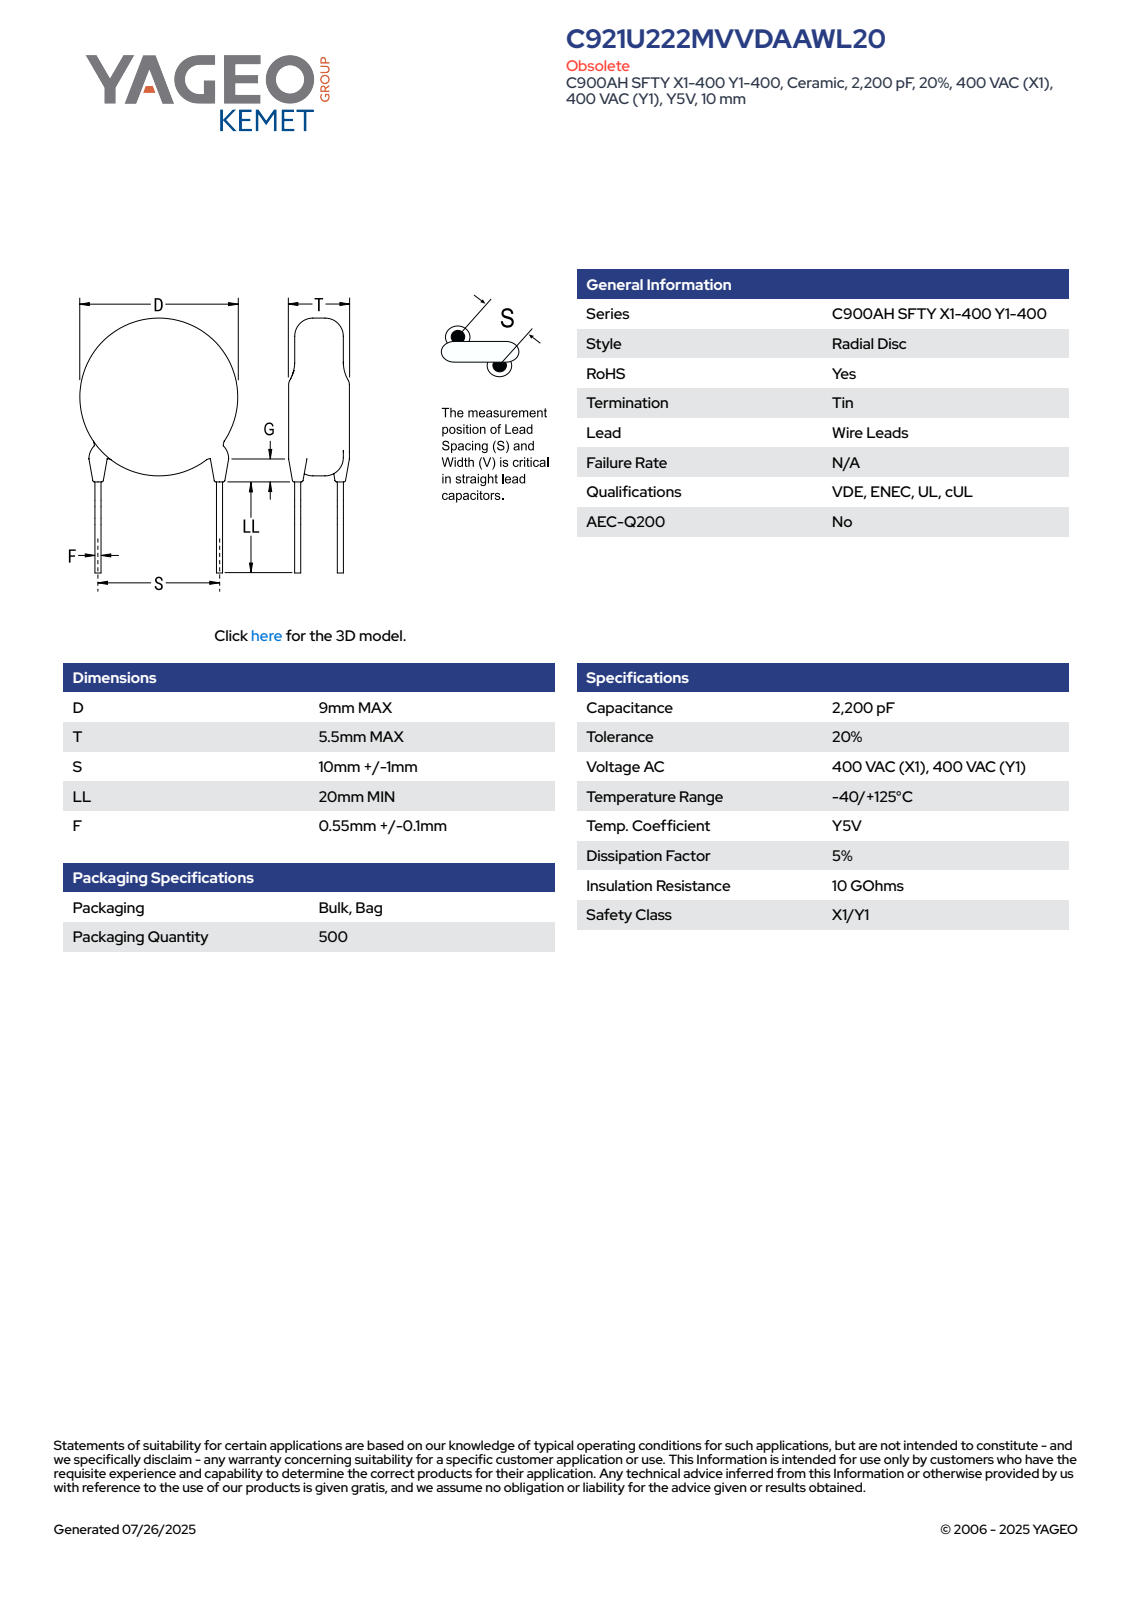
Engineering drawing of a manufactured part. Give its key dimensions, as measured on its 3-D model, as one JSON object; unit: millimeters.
{"part_name": "CCD_STC900_D9T5.5S10LL20F0.65G3", "step_written_by": "SolidWorks 2014 (AUTOMOTIVE_DESIGN)", "units": "millimeters", "bodies": {"solids": 4, "faces": 83, "planar": 61, "cylindrical": 6, "other": 16}, "overall_size": [29.38, 10.15, 5.5], "volume_mm3": 356, "surface_area_mm2": 360, "round_bosses_or_shafts": [[0.65, 2], [9, 1]], "face_to_face_distances": [5.5, 1.04, 25.4, 24.36, 0.84, 0.45, 0.39, 2.14, 3.08, 3.2]}
